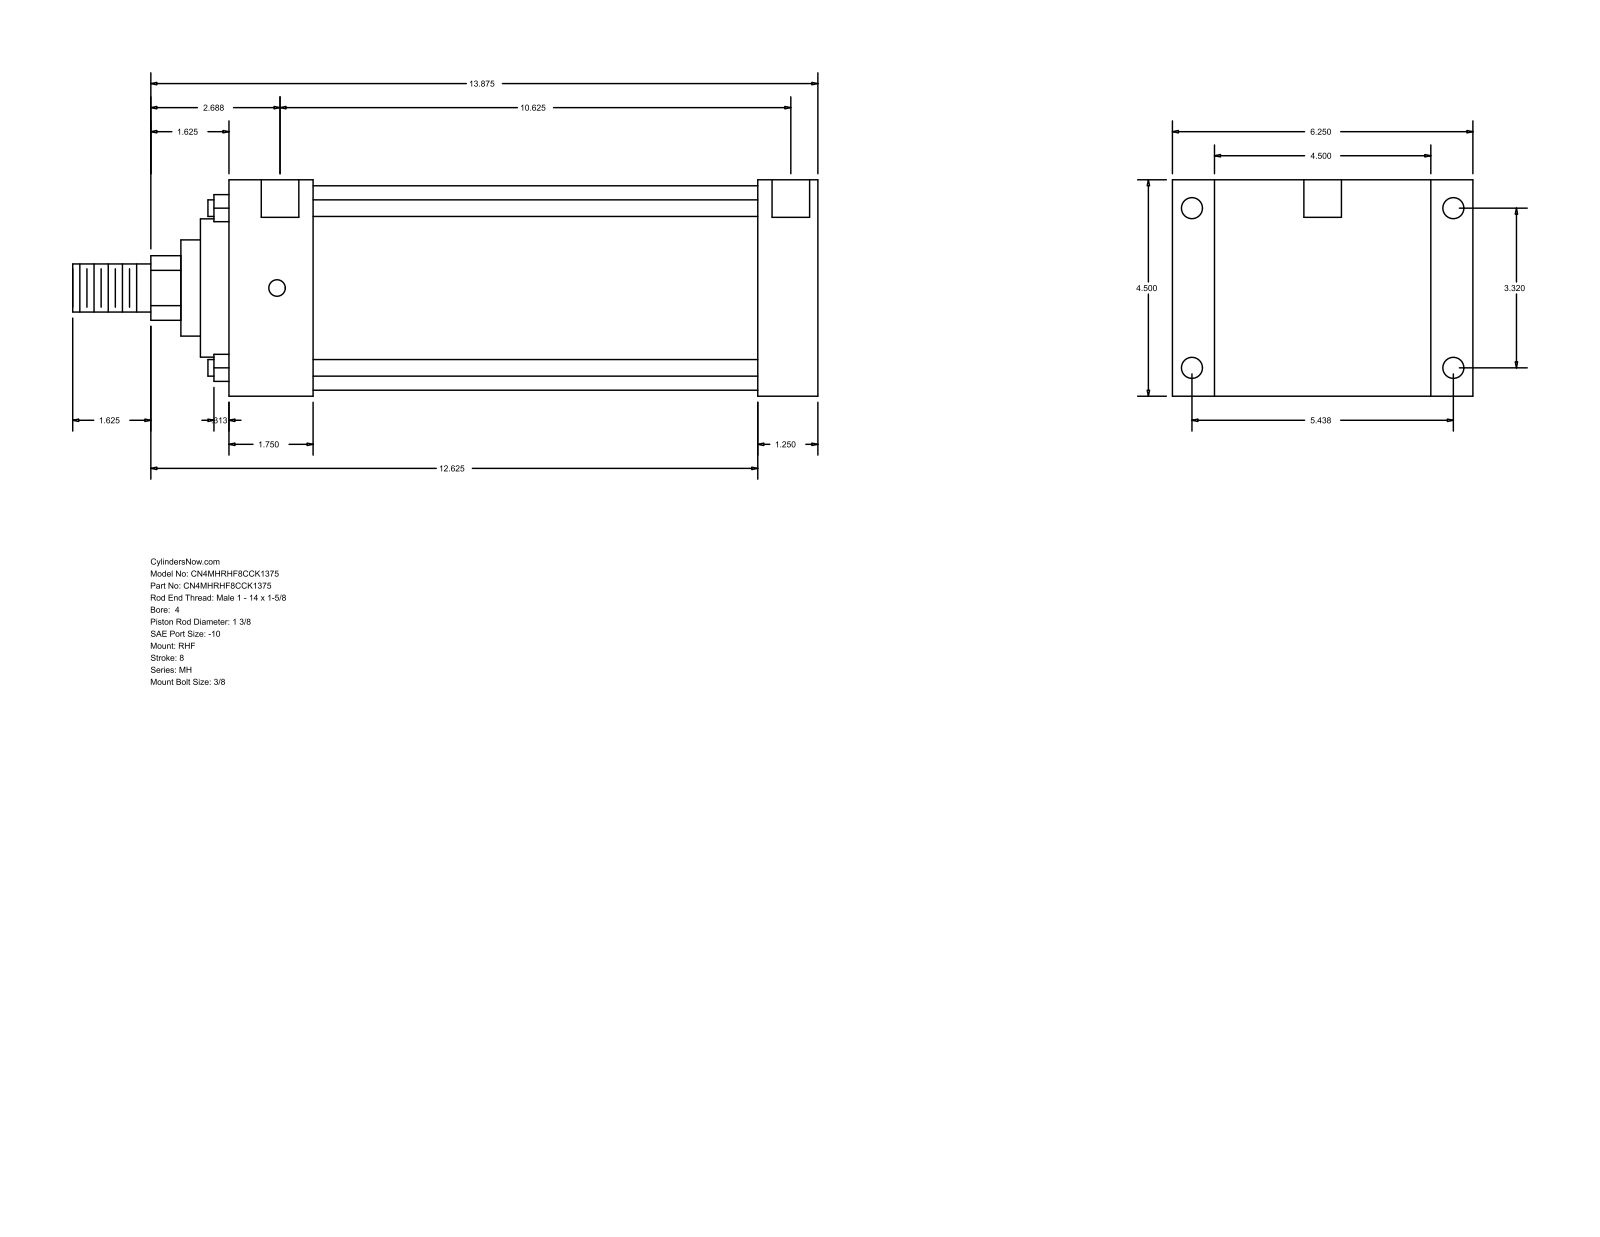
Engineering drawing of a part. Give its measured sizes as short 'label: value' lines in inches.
name: MH_RHF__0400_1.375
written by: GSSL Pune (CONFIG_CONTROL_DESIGN)
unit: in
bodies: 0 solids, 90 faces (61 planar, 29 cylindrical, 0 other)
size: 15.5 × 6.25 × 4.5
holes: 4× ⌀0.344, 4× ⌀0.438, 2× ⌀0.781
bosses: 4× ⌀0.345, 1× ⌀4.25, 1× ⌀2.875, 1× ⌀2, 1× ⌀1.375, 1× ⌀1
rounds: 1× R0.672
face distances: 4.5, 1.25, 11, 12.25, 0.875, 5.375, 1.75, 9.25, 10.5, 6.25
hole spacings: 0.063, 3.32, 5.438, 6.371, 10.688, 10.75, 10.625
